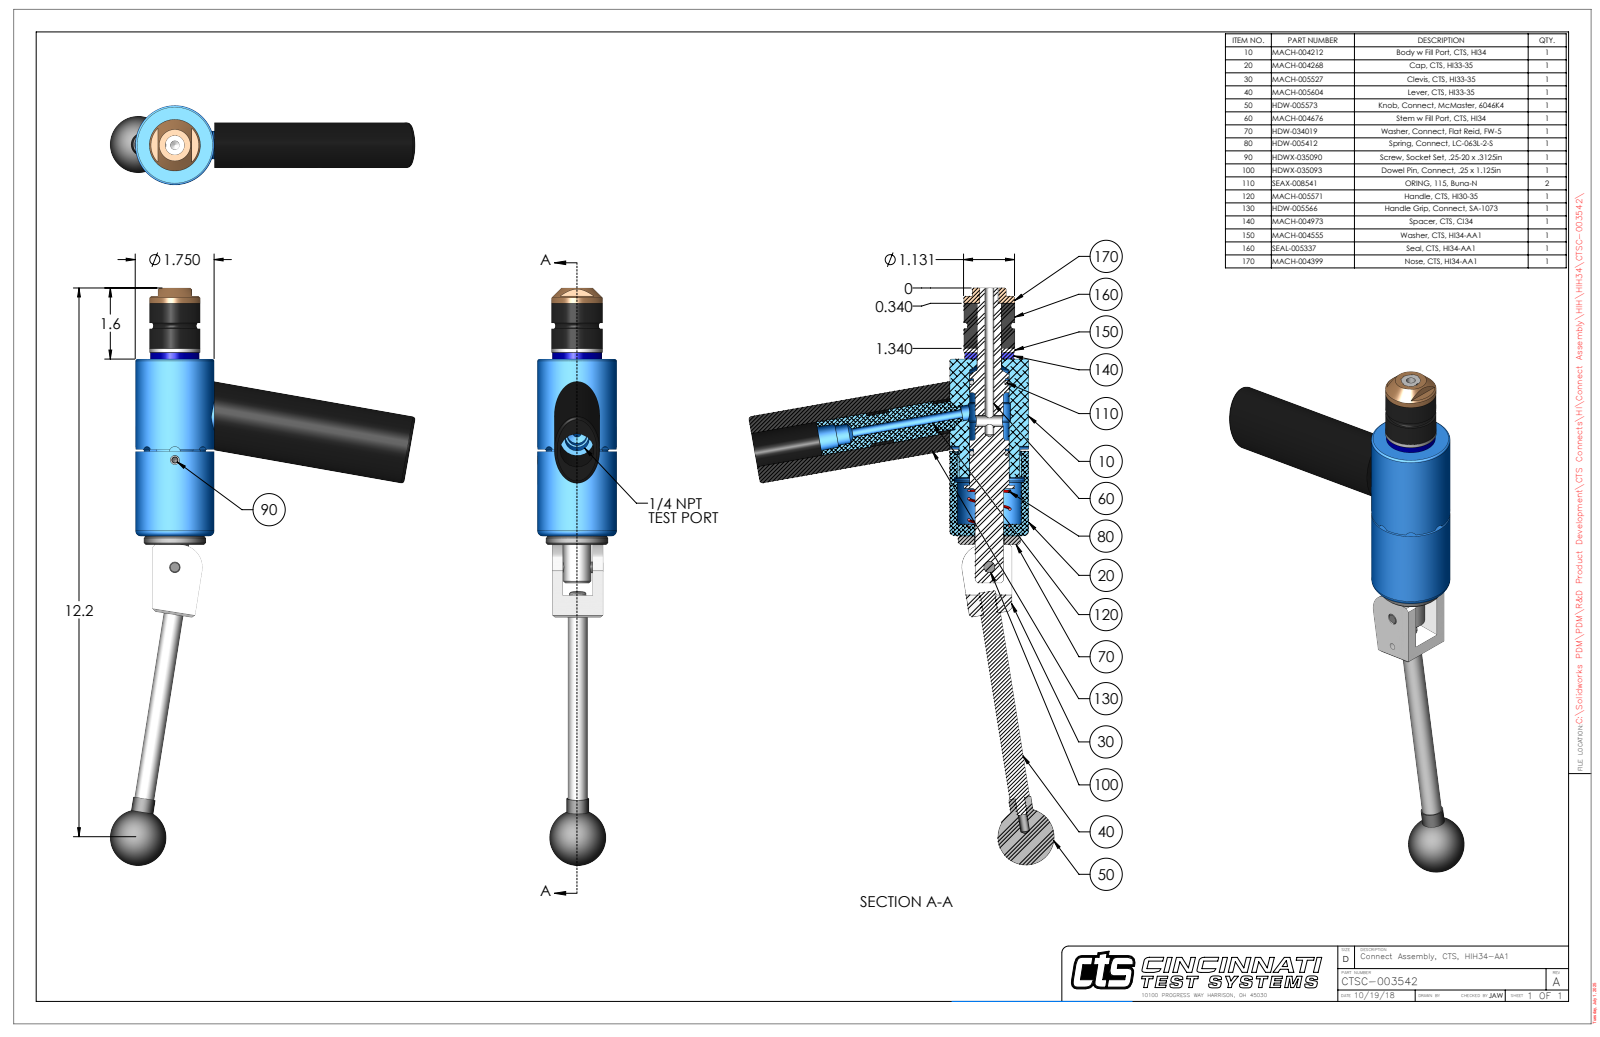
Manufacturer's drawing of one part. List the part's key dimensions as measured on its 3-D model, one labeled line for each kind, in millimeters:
Part name (STEP PRODUCT): CTSC-003542
STEP written by: SolidWorks 2023 (AUTOMOTIVE_DESIGN)
Units: millimetres
Bodies: 11 solids, 305 faces (109 planar, 126 cylindrical, 70 other)
Overall size (bounding box): 325 × 171.8 × 44.5
Volume: 298 600 mm³ · Surface area: 74 900 mm²
Round holes (diameter × count): ⌀5.1 ×2, ⌀3.8 ×1, ⌀4.7 ×1, ⌀5.2 ×1, ⌀6.3 ×1, ⌀6.4 ×1, ⌀6.4 ×1, ⌀8 ×1, ⌀10.7 ×1, ⌀11.1 ×1, ⌀13.5 ×1, ⌀13.7 ×1
Round bosses / shafts (diameter × count): ⌀12.7 ×2, ⌀11.2 ×2, ⌀6.4 ×2, ⌀44.5 ×1, ⌀35.1 ×1, ⌀28.7 ×1, ⌀27.7 ×1, ⌀19.1 ×1
Partial cylindrical surfaces — rounded edges, fillets, slot ends (radius × count): R3.2 ×4, R0.7 ×2, R4.2 ×1, R4.6 ×1, R8.4 ×1, R12.7 ×1, R17.7 ×1, R20.7 ×1
Main face-to-face distances: 99.6, 31.4, 131, 25.4, 6, 105.6, 28.4, 27.8, 2.4, 3.6
Hole centre spacings: 18.8, 60.4, 79.1
